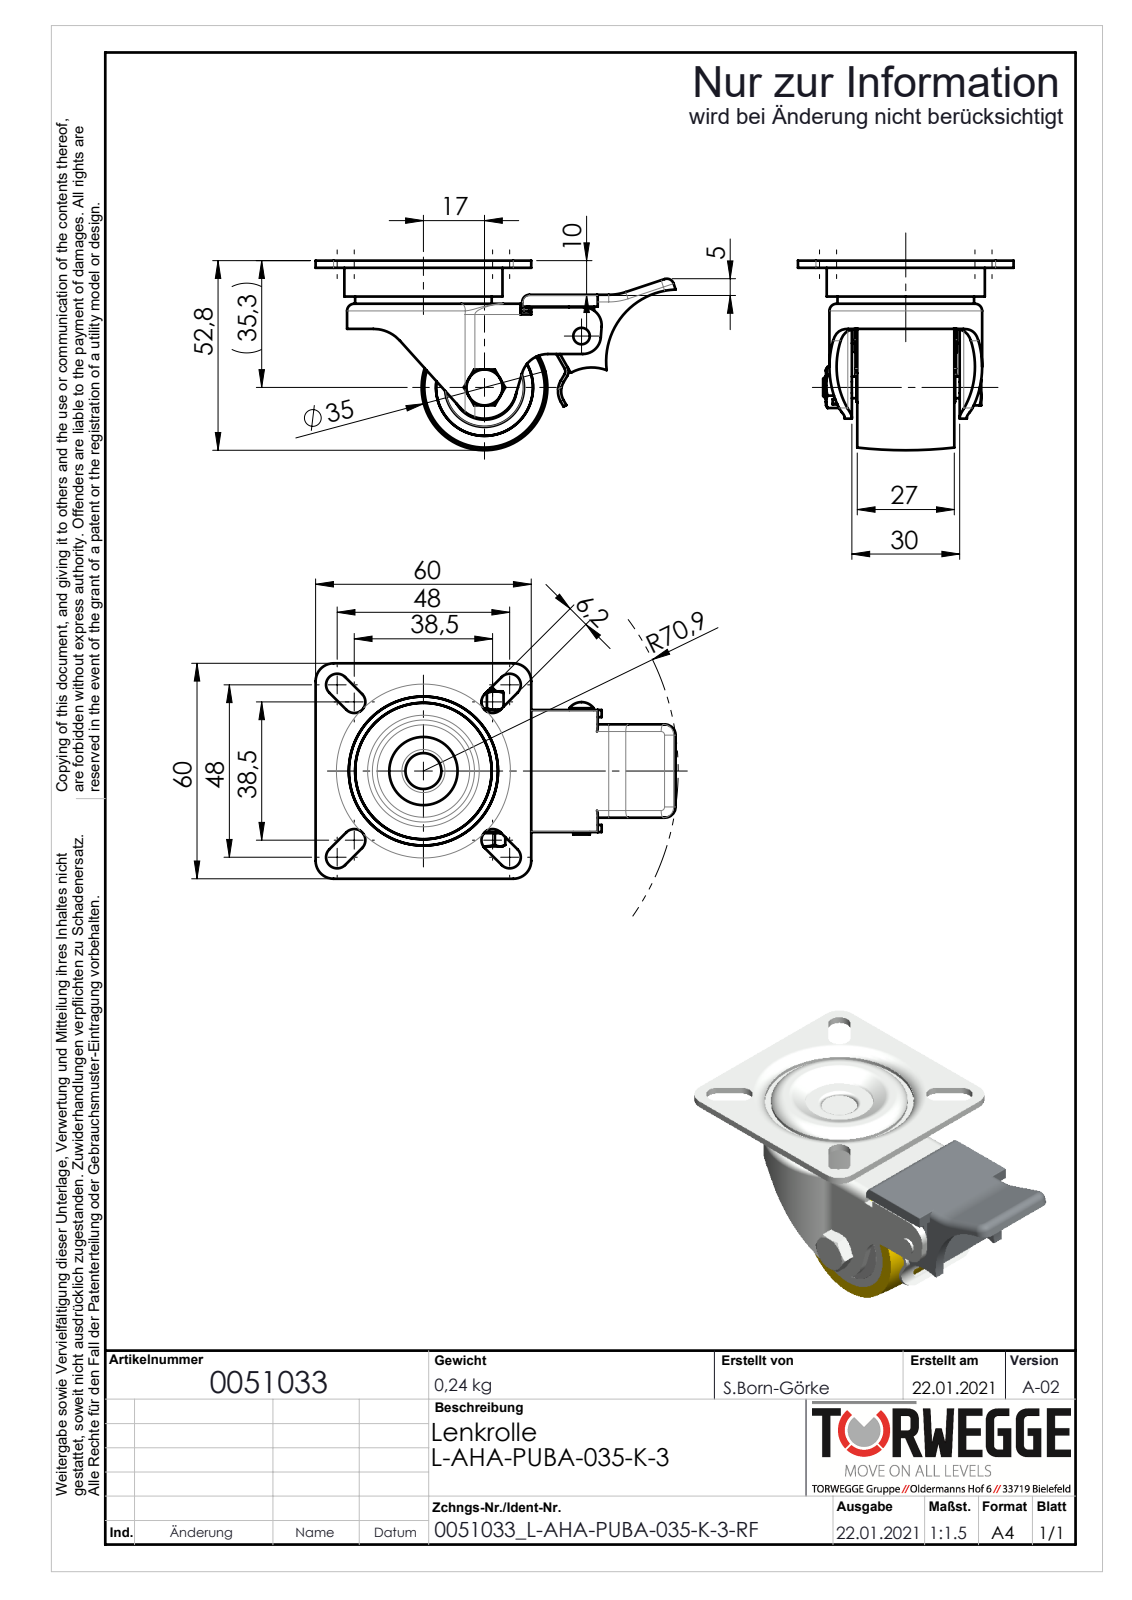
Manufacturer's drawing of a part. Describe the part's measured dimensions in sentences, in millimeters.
The part is named "0051033". Its 3-D file was written by "SolidWorks 2018 (AUTOMOTIVE_DESIGN)". It is 21 solids with 445 faces: 164 planar, 181 cylindrical and 100 other. Overall it measures 100.19 by 60 by 52.8 millimeters. Its volume is 48 385 cubic millimeters and its surface area 46 557 square millimeters. Round holes: 1 of diameter 4.2, 1 of diameter 5, 1 of diameter 6, 1 of diameter 6.2, 1 of diameter 8, 1 of diameter 8.6, 1 of diameter 18, 1 of diameter 27, 1 of diameter 34, 1 of diameter 40, 1 of diameter 41.5. Round bosses or shafts: 1 of diameter 44, 1 of diameter 38, 1 of diameter 23, 1 of diameter 22, 1 of diameter 12, 1 of diameter 10, 1 of diameter 7.95, 1 of diameter 6.8. Partial cylindrical surfaces (rounded edges, fillets, slot ends): 11 of radius 5, 8 of radius 1, 8 of radius 3.1, 7 of radius 0.2, 6 of radius 2, 5 of radius 3, 4 of radius 0.5, 2 of radius 1.6. The main face-to-face distances are 2, 4, 1.5, 0.5, 3.5, 10, 30.5, 1, 3, 7. The hole center spacings are 30.55.
